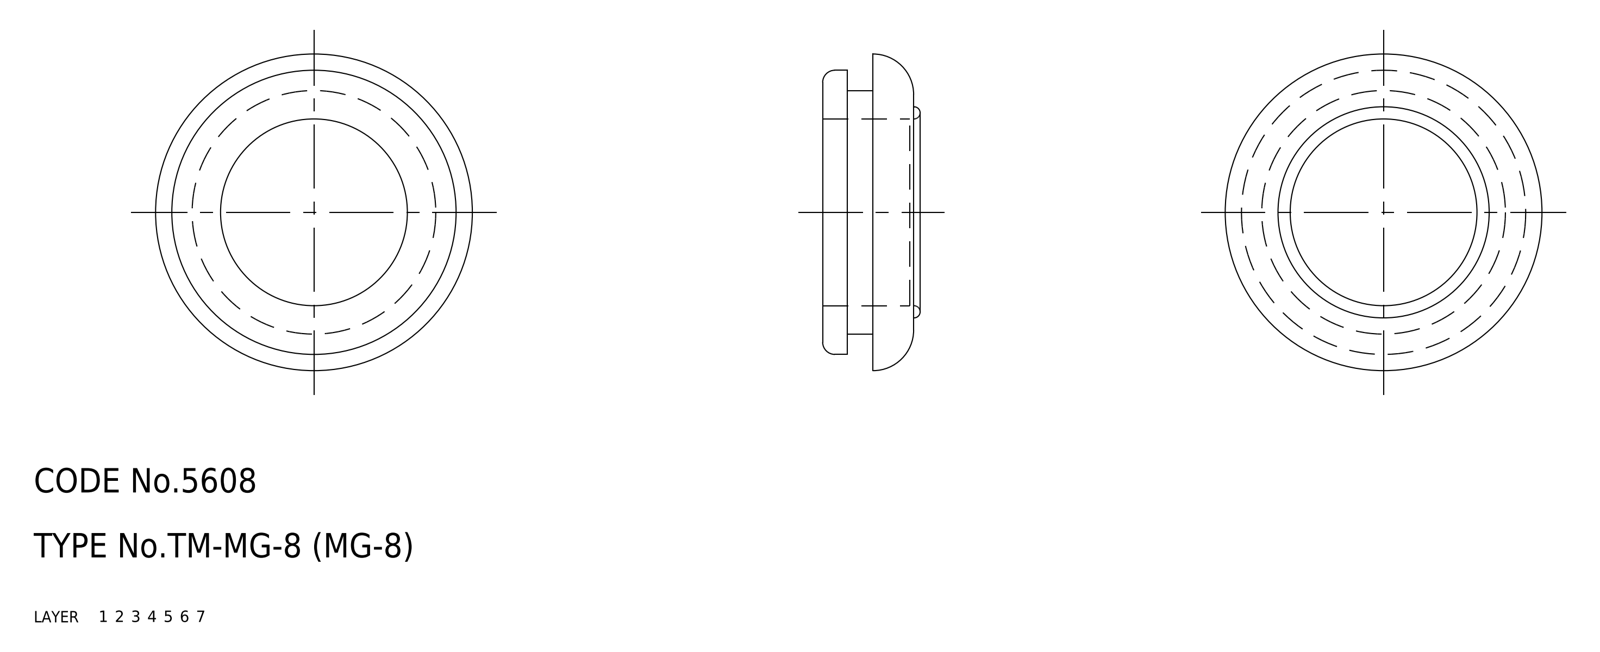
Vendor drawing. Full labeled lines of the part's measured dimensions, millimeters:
Part name (STEP PRODUCT): grommet; TM_MG_8
STEP written by: SolidWorks 2015 (AUTOMOTIVE_DESIGN)
Units: millimetres
Bodies: 1 solid, 22 faces (6 planar, 10 cylindrical, 6 other)
Overall size (bounding box): 39 × 39 × 12
Volume: 6 078 mm³ · Surface area: 4 645 mm²
Round holes (diameter × count): ⌀23 ×1
Round bosses / shafts (diameter × count): ⌀35 ×1, ⌀30 ×1, ⌀26 ×1
Main face-to-face distances: 5, 0.5, 4.5, 11.2, 10.7, 6.2, 8.2, 7.7, 3.2, 3
